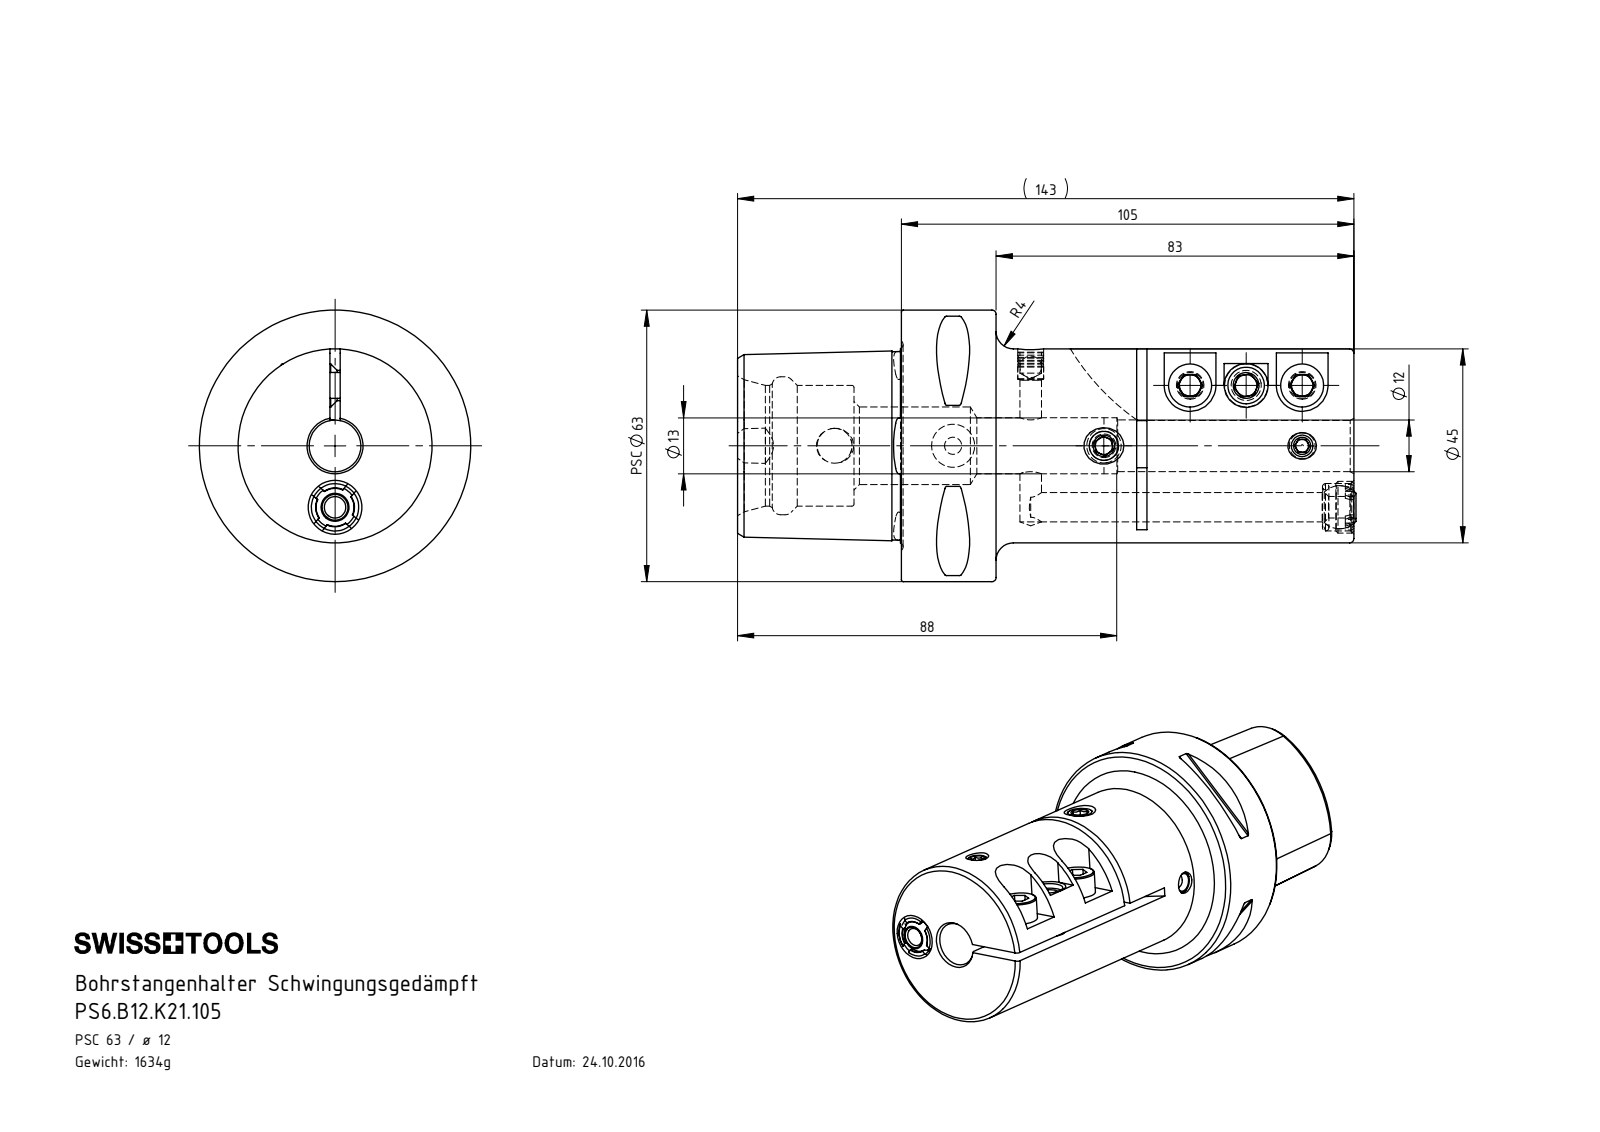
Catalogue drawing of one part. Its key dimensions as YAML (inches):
part_name: "KU1-U12.002.010_A; KVT_MB_600_060; PS6-B12.K21.105_A; ISO 4028 - M8 x 16 (+7 more)"
step_written_by: "SolidWorks 2015 (CONFIG_CONTROL_DESIGN)"
units: inches
bodies: {solids: 11, faces: 425, planar: 127, cylindrical: 105, other: 193}
overall_size: [5.649, 2.48, 2.48]
volume: 12.75
surface_area: 70.11
round_holes:
  - {diameter: 0.197, count: 5}
  - {diameter: 0.157, count: 2}
  - {diameter: 0.252, count: 2}
  - {diameter: 0.268, count: 2}
  - {diameter: 0.319, count: 1}
  - {diameter: 0.335, count: 1}
  - {diameter: 0.394, count: 1}
  - {diameter: 0.433, count: 1}
  - {diameter: 0.472, count: 1}
  - {diameter: 0.512, count: 1}
  - {diameter: 0.709, count: 1}
  - {diameter: 1.102, count: 1}
round_bosses_or_shafts:
  - {diameter: 0.236, count: 4}
  - {diameter: 0.394, count: 3}
  - {diameter: 2.48, count: 1}
  - {diameter: 1.772, count: 1}
  - {diameter: 0.472, count: 1}
  - {diameter: 0.315, count: 1}
  - {diameter: 0.276, count: 1}
  - {diameter: 0.217, count: 1}
partial_cylinders:
  - {radius: 0.02, count: 8}
  - {radius: 0.217, count: 2}
  - {radius: 0.173, count: 1}
  - {radius: 0.201, count: 1}
  - {radius: 0.236, count: 1}
  - {radius: 2.047, count: 1}
  - {radius: 2.165, count: 1}
face_to_face_distances: [0.094, 4.134, 0.866, 3.268, 2.15, 1.283, 1.984, 2.244, 1.378, 1.89]
hole_center_spacings: [0.512, 0.551, 0.561, 0.752, 0.961, 1.024, 1.083, 1.163]
